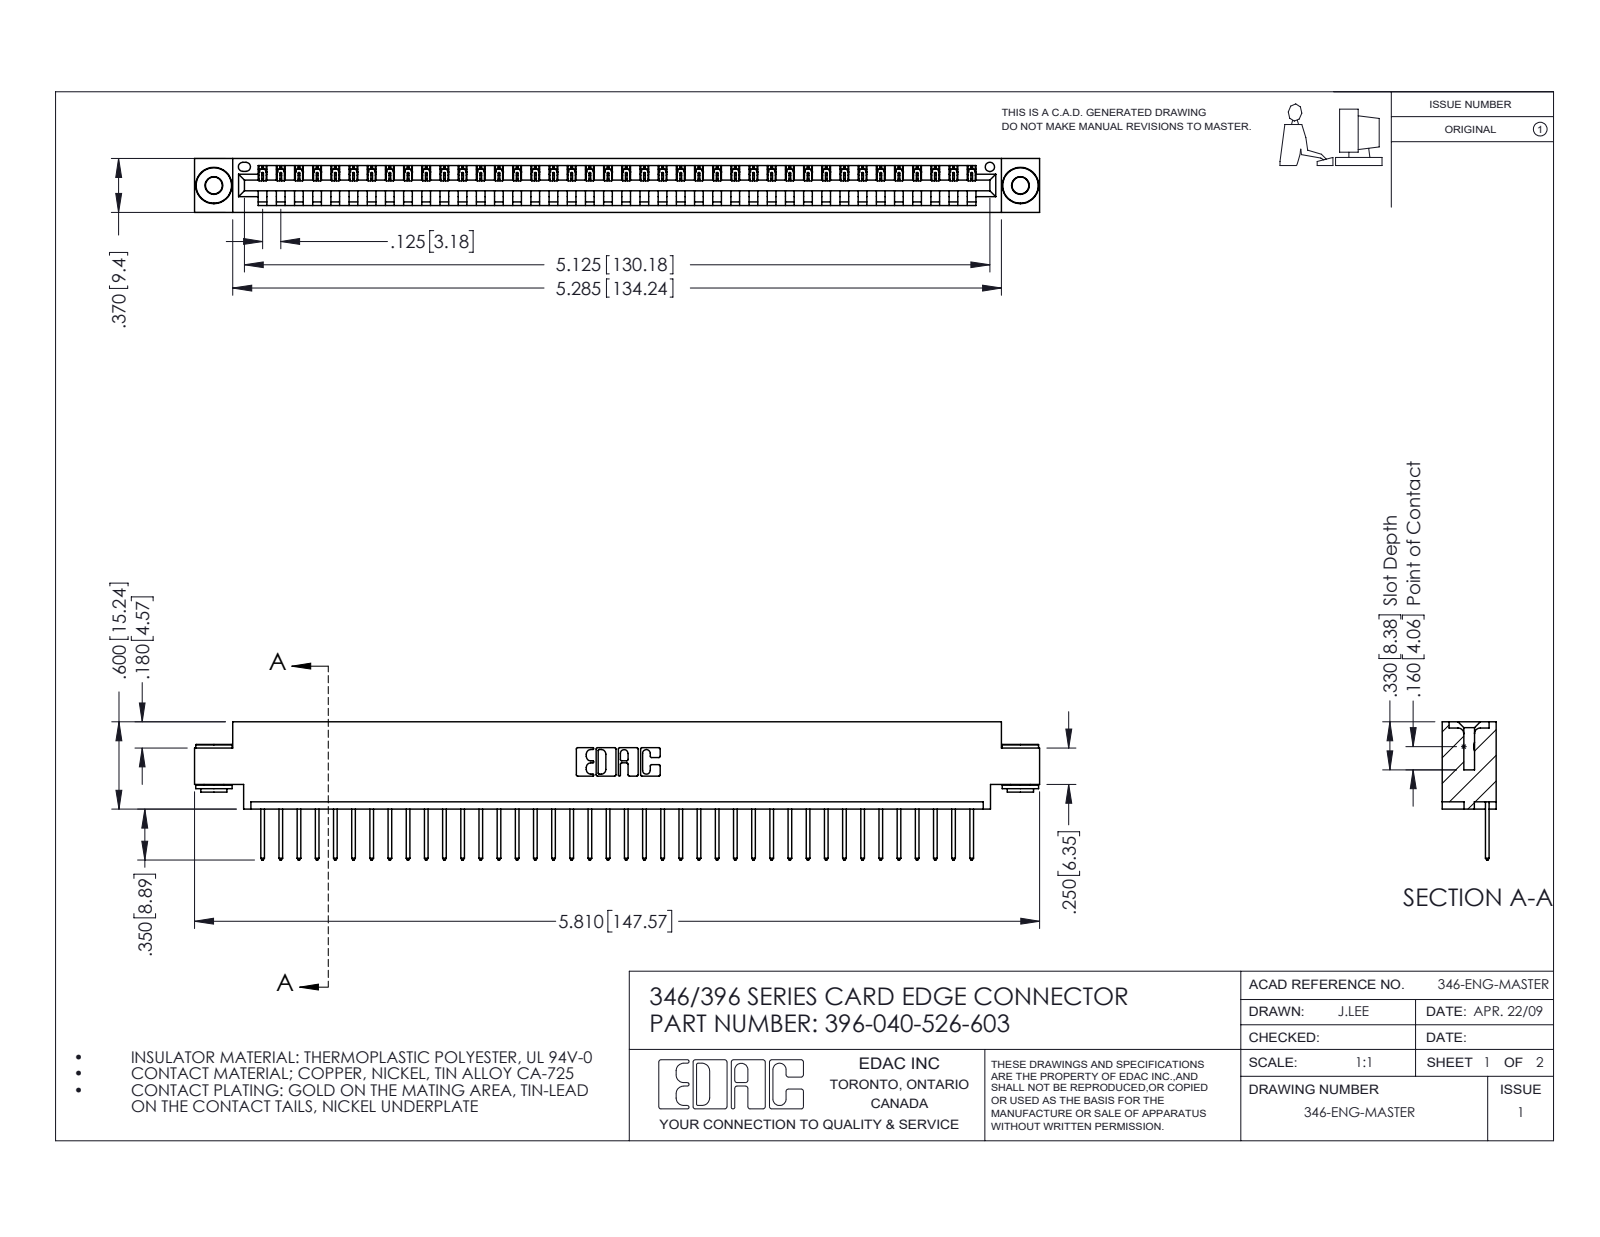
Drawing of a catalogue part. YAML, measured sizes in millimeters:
part_name: "396-040-526-603; 345-292-001_345-293-126; 346 Part_0.170 Offset - 0.156 Dia-TH; 345-250-002_345-250-002-102"
step_written_by: "SolidWorks 2016 (CONFIG_CONTROL_DESIGN)"
units: millimeters
bodies: {solids: 43, faces: 2484, planar: 1690, cylindrical: 786, other: 8}
overall_size: [147.6, 24.1, 9.4]
volume: 13900
surface_area: 17750
round_holes:
  - {diameter: 2.9, count: 2}
  - {diameter: 4, count: 2}
  - {diameter: 1.6, count: 1}
round_bosses_or_shafts:
  - {diameter: 6.4, count: 2}
  - {diameter: 4.6, count: 2}
  - {diameter: 3.5, count: 2}
partial_cylinders:
  - {radius: 0.2, count: 80}
  - {radius: 0.3, count: 80}
  - {radius: 0.3, count: 22}
  - {radius: 0.2, count: 6}
  - {radius: 0.8, count: 6}
  - {radius: 0.7, count: 3}
  - {radius: 0.8, count: 2}
  - {radius: 1, count: 2}
face_to_face_distances: [1.2, 8.2, 9.4, 6.4, 0.6, 1.8, 7.6, 3.8, 5.6, 2.5]
hole_center_spacings: [6.2, 135.5, 140.8]
